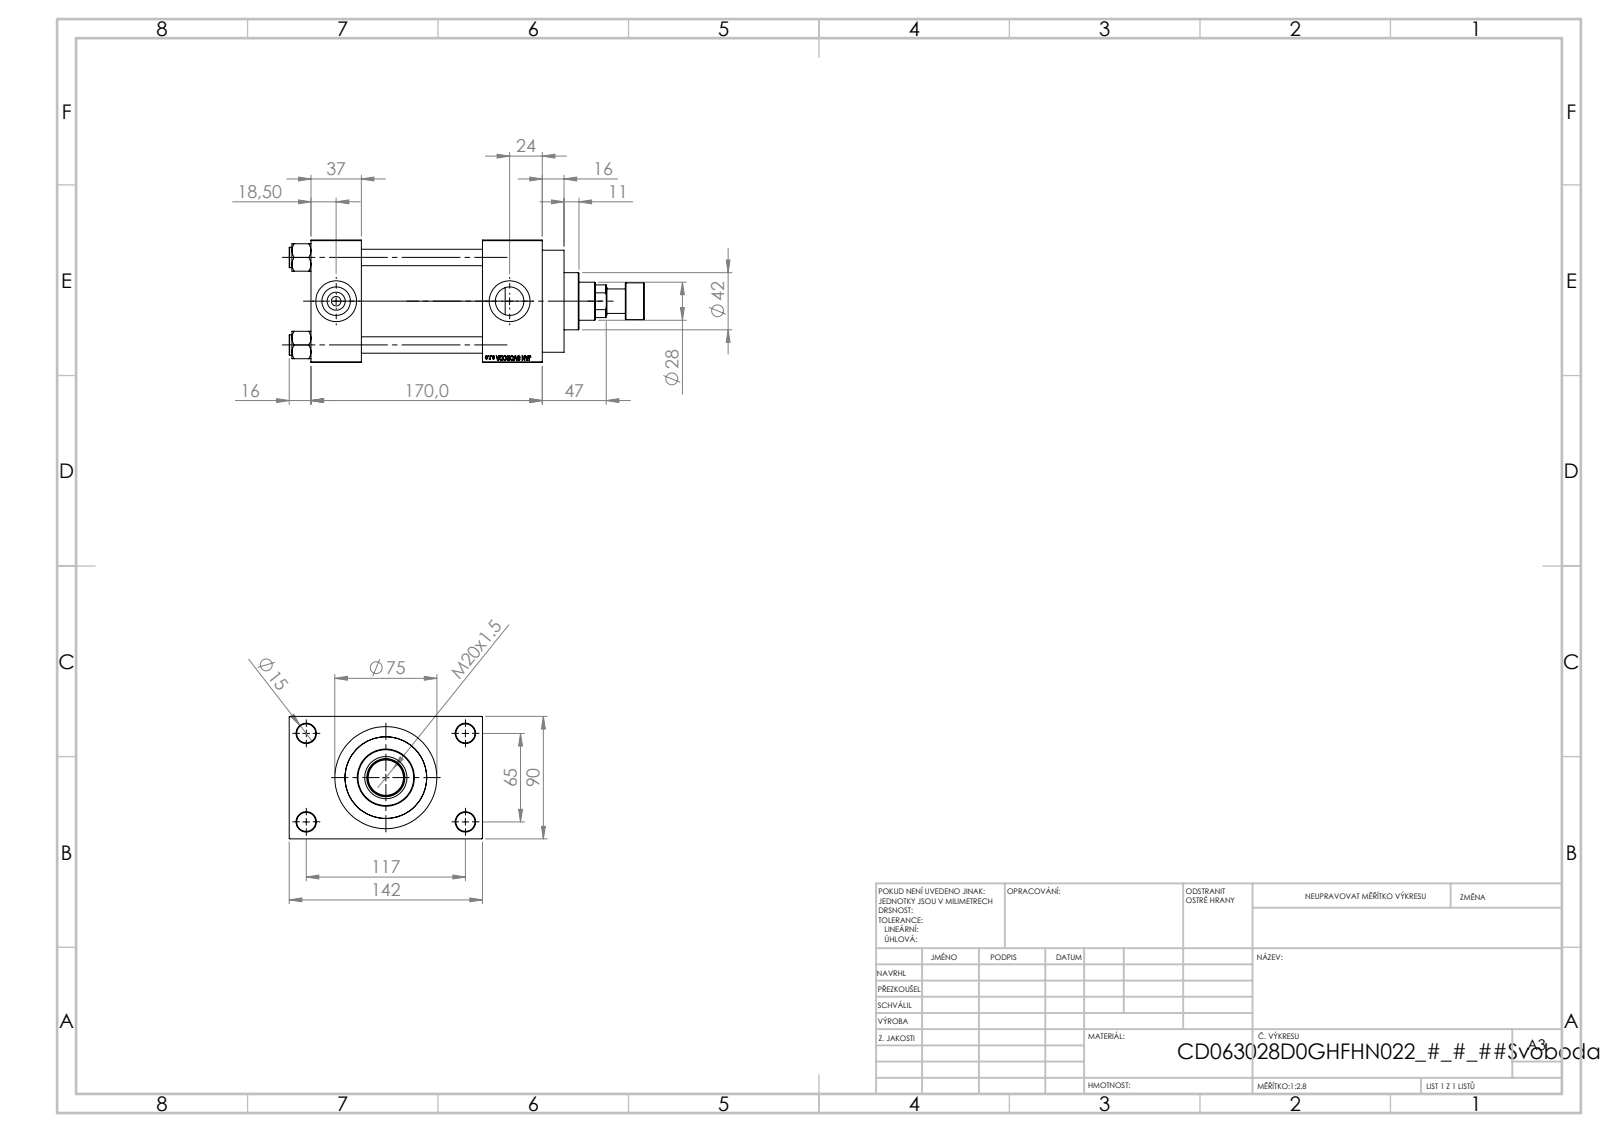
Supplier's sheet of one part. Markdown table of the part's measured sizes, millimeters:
| quantity | value |
| --- | --- |
| part name | V215CR_ROD_END_F; V215CD_VC_A; V215CD_D_Body; V215CD_D_TYCINKA (+2 more) |
| STEP written by | SolidWorks 2019 (CONFIG_CONTROL_DESIGN) |
| units | millimeters |
| bodies | 12 solids, 1117 faces (501 planar, 92 cylindrical, 524 other) |
| overall size | 261 × 142 × 90 |
| volume | 1 159 000 mm³ |
| surface area | 223 174 mm² |
| round holes (diameter × count) | 12 × 4, 14 × 4, 7 × 2, 20.96 × 2, 30 × 2, 18.5 × 1, 28 × 1, 31 × 1, 50 × 1, 60 × 1, 63 × 1 |
| round bosses / shafts (diameter × count) | 15 × 4, 75 × 1, 69 × 1, 42 × 1, 27 × 1, 18 × 1 |
| main face-to-face distances | 90, 89, 37, 126, 133, 170, 44, 26, 116, 142 |
| hole center spacings | 26.35, 45.47, 64.3, 66.92, 69.81, 90.65, 111.34, 65 |
